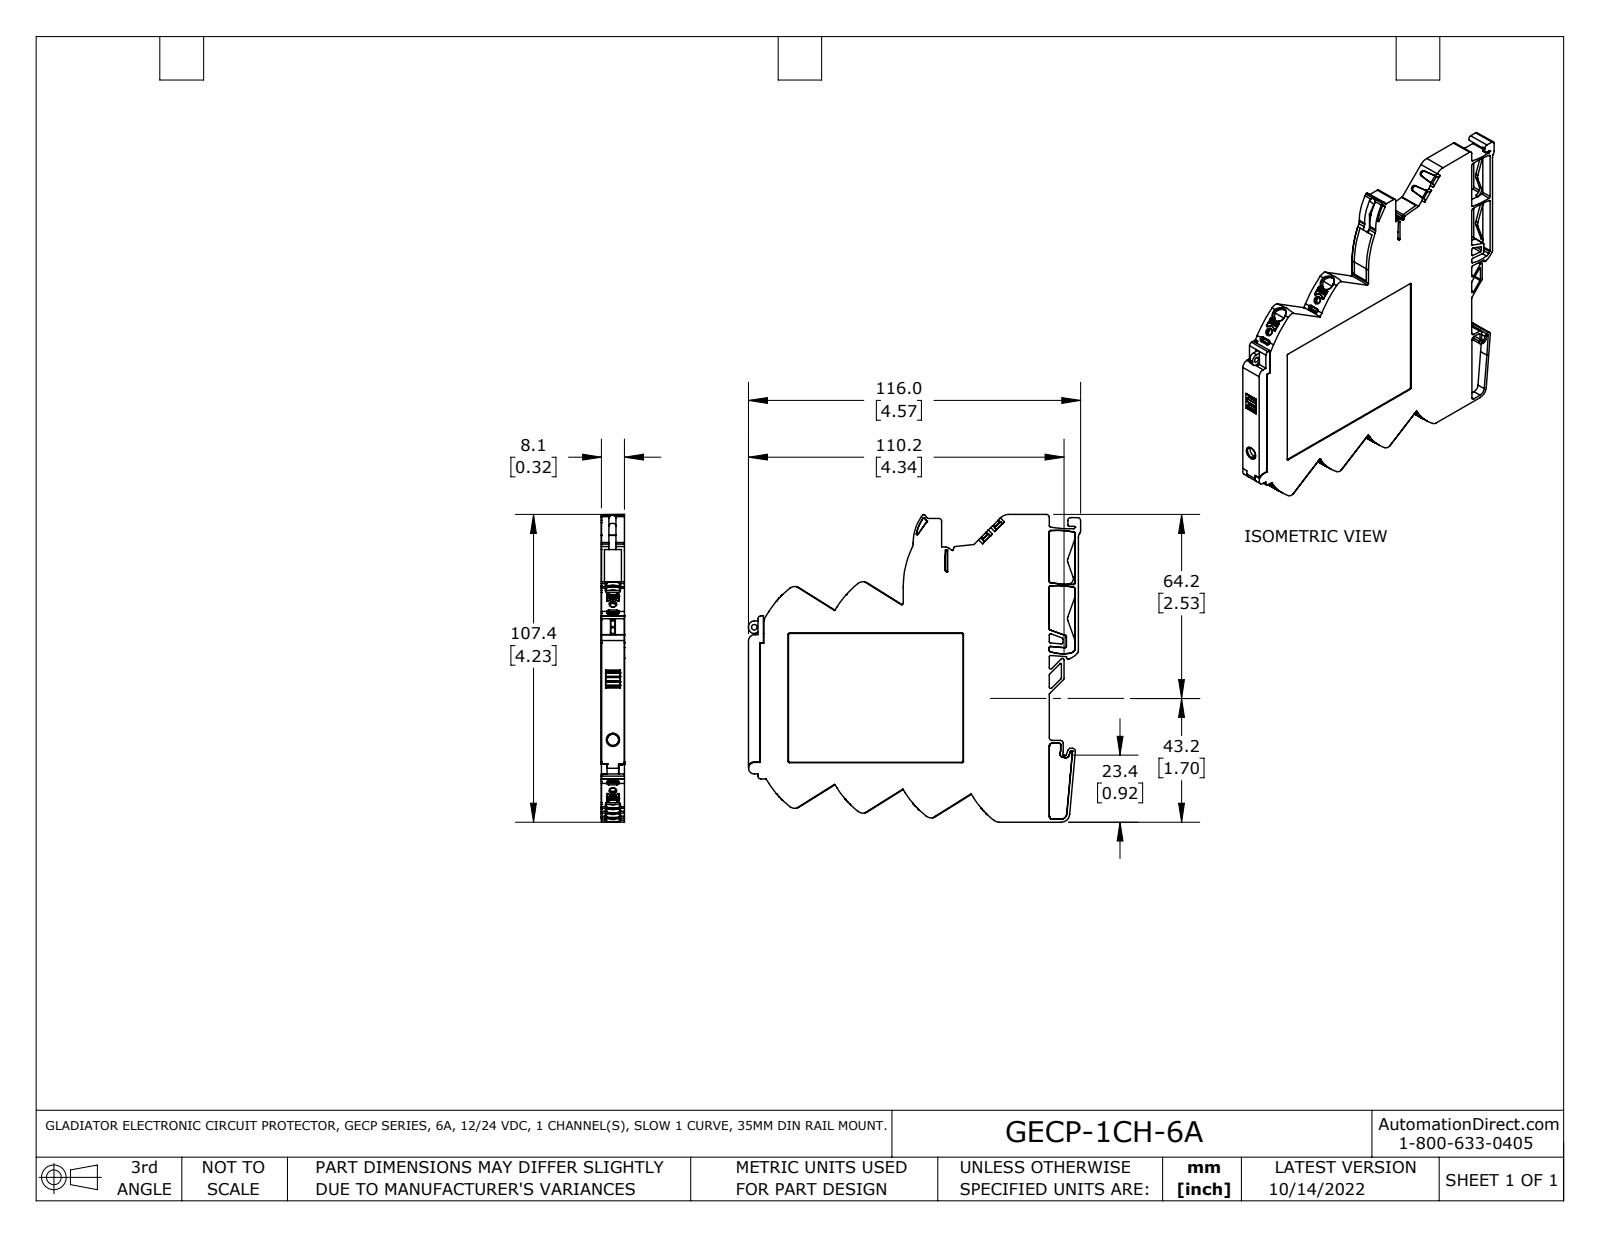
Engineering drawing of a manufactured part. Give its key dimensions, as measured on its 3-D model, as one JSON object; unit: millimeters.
{"part_name": "GECP-1CH-6A", "step_written_by": "SolidWorks 2021 (AUTOMOTIVE_DESIGN)", "units": "millimeters", "bodies": {"solids": 1, "faces": 1182, "planar": 549, "cylindrical": 466, "other": 167}, "overall_size": [116, 107.7, 8.1], "volume_mm3": 71140, "surface_area_mm2": 30140, "round_holes": [[2.1, 6], [2, 1], [2.2, 1]], "round_bosses_or_shafts": [[2.1, 1]], "partial_cylinders_radius": [[0.5, 58], [1, 45], [0.2, 43], [0.3, 28], [0.3, 27], [2, 13], [0.2, 12], [33, 12]], "face_to_face_distances": [8.1, 7.9, 7.8, 8.1, 5.1, 4, 3, 9, 99.9, 104], "hole_center_spacings": [14.2, 28.4, 14.2, 42.6, 49.2]}
